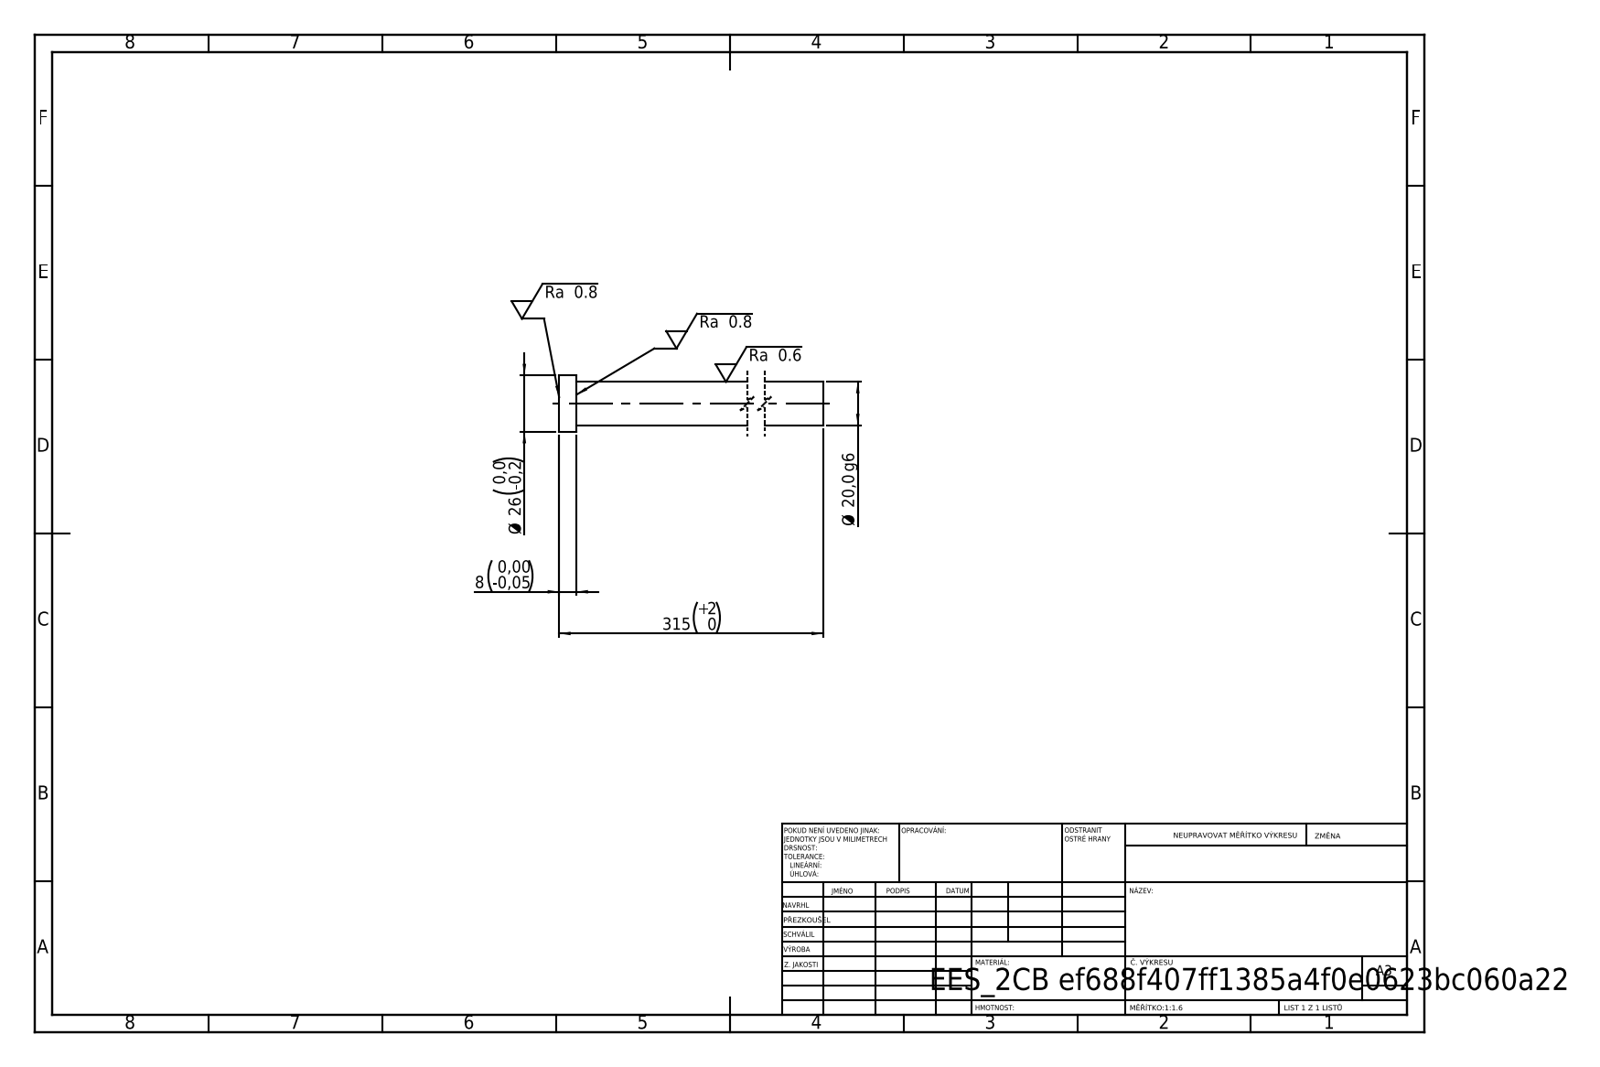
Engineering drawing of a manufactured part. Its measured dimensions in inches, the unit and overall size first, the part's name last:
Units: inches
Overall size (bounding box): 12.402 × 1.024 × 1.024
Round bosses / shafts (diameter × count): ⌀1.024 ×1, ⌀0.787 ×1
Main face-to-face distances: 12.402, 0.315, 12.087
Volume: 6.145 in³ · Surface area: 32.56 in²
Bodies: 1 solid, 7 faces (3 planar, 4 cylindrical, 0 other)
STEP written by: SolidWorks 2019 (CONFIG_CONTROL_DESIGN)
